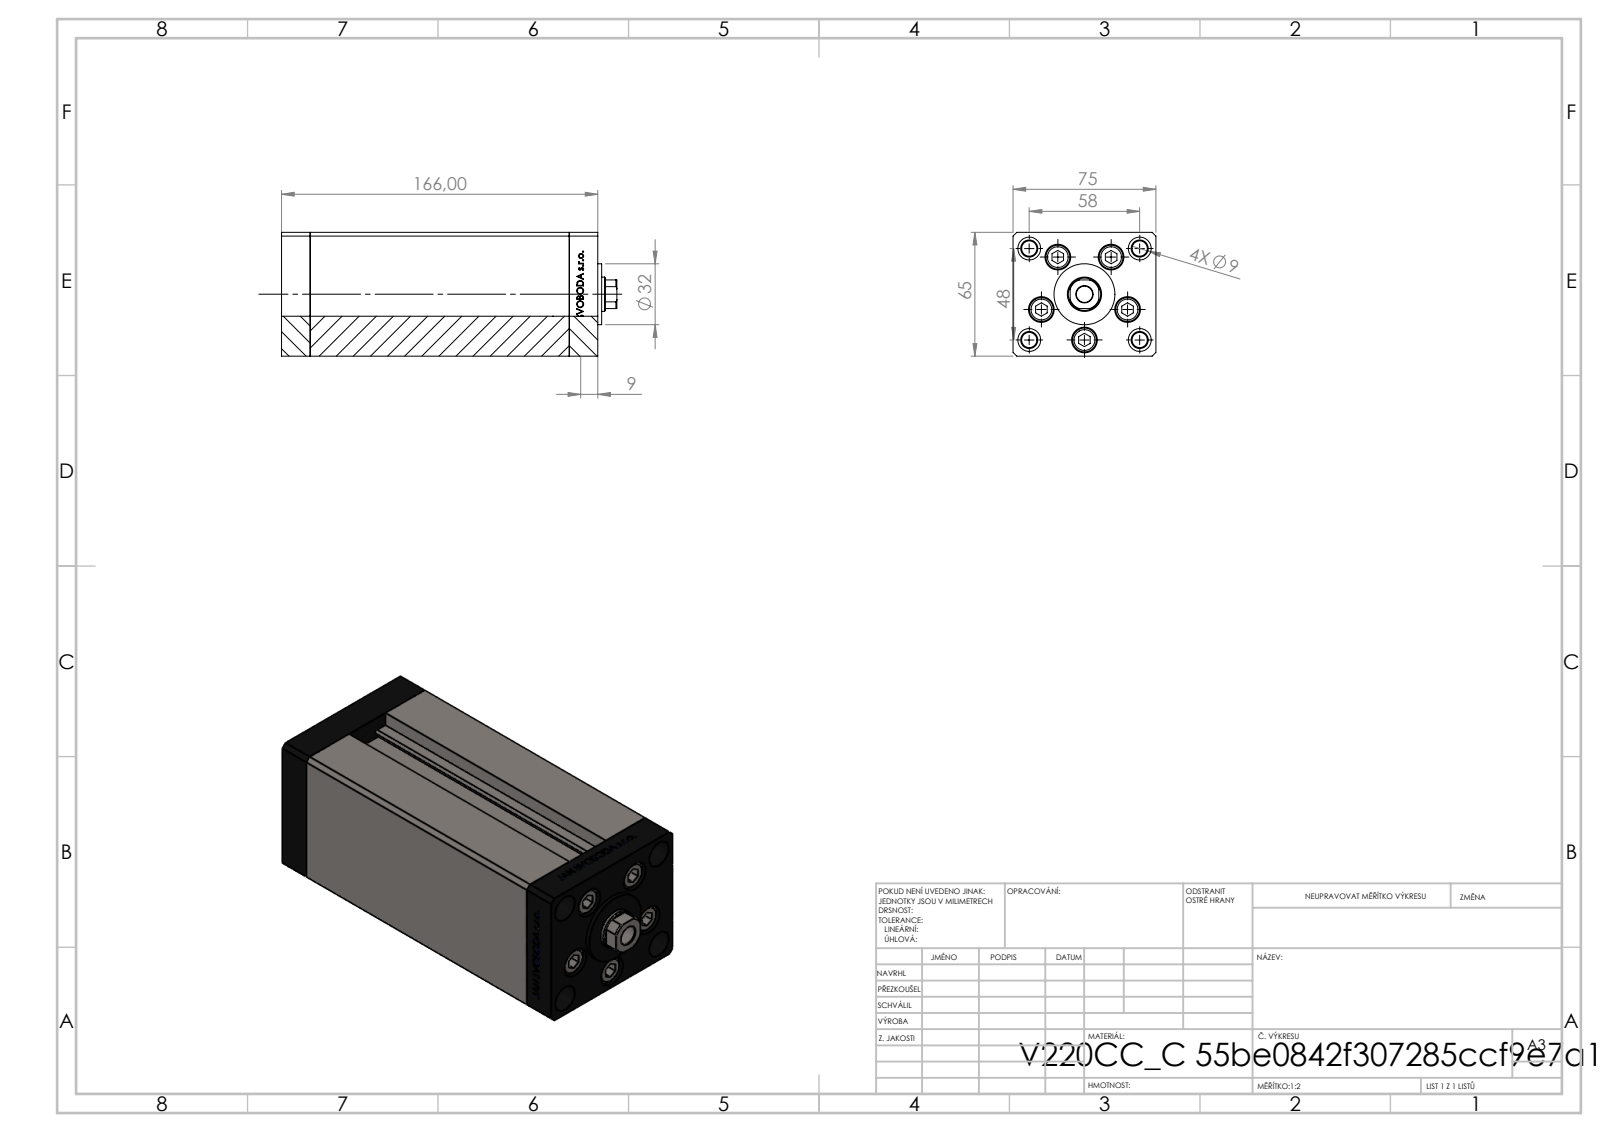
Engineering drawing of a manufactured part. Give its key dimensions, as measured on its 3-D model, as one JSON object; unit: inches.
{"part_name": "ALLEN BOLT; V220C_VC_C; V220C_C MIDDLE; V220C BACK_C (+1 more)", "step_written_by": "SolidWorks 2019 (CONFIG_CONTROL_DESIGN)", "units": "inches", "bodies": {"solids": 13, "faces": 1159, "planar": 538, "cylindrical": 159, "other": 462}, "overall_size": [6.929, 2.953, 2.559], "volume_in3": 41.75, "surface_area_in2": 219, "round_holes": [[0.354, 9], [0.531, 5], [0.315, 4], [0.472, 4], [0.335, 1], [0.492, 1], [0.709, 1]], "round_bosses_or_shafts": [[0.315, 5], [0.492, 4], [1.26, 1]], "partial_cylinders_radius": [[0.037, 2], [0.335, 1]], "face_to_face_distances": [2.953, 2.559, 0.591, 5.354, 5.945, 6.535, 1.102, 5.591, 0.354, 2.146], "hole_center_spacings": [0.945, 1.482, 0.617, 0.678, 1.091, 1.135, 1.142, 1.285]}
